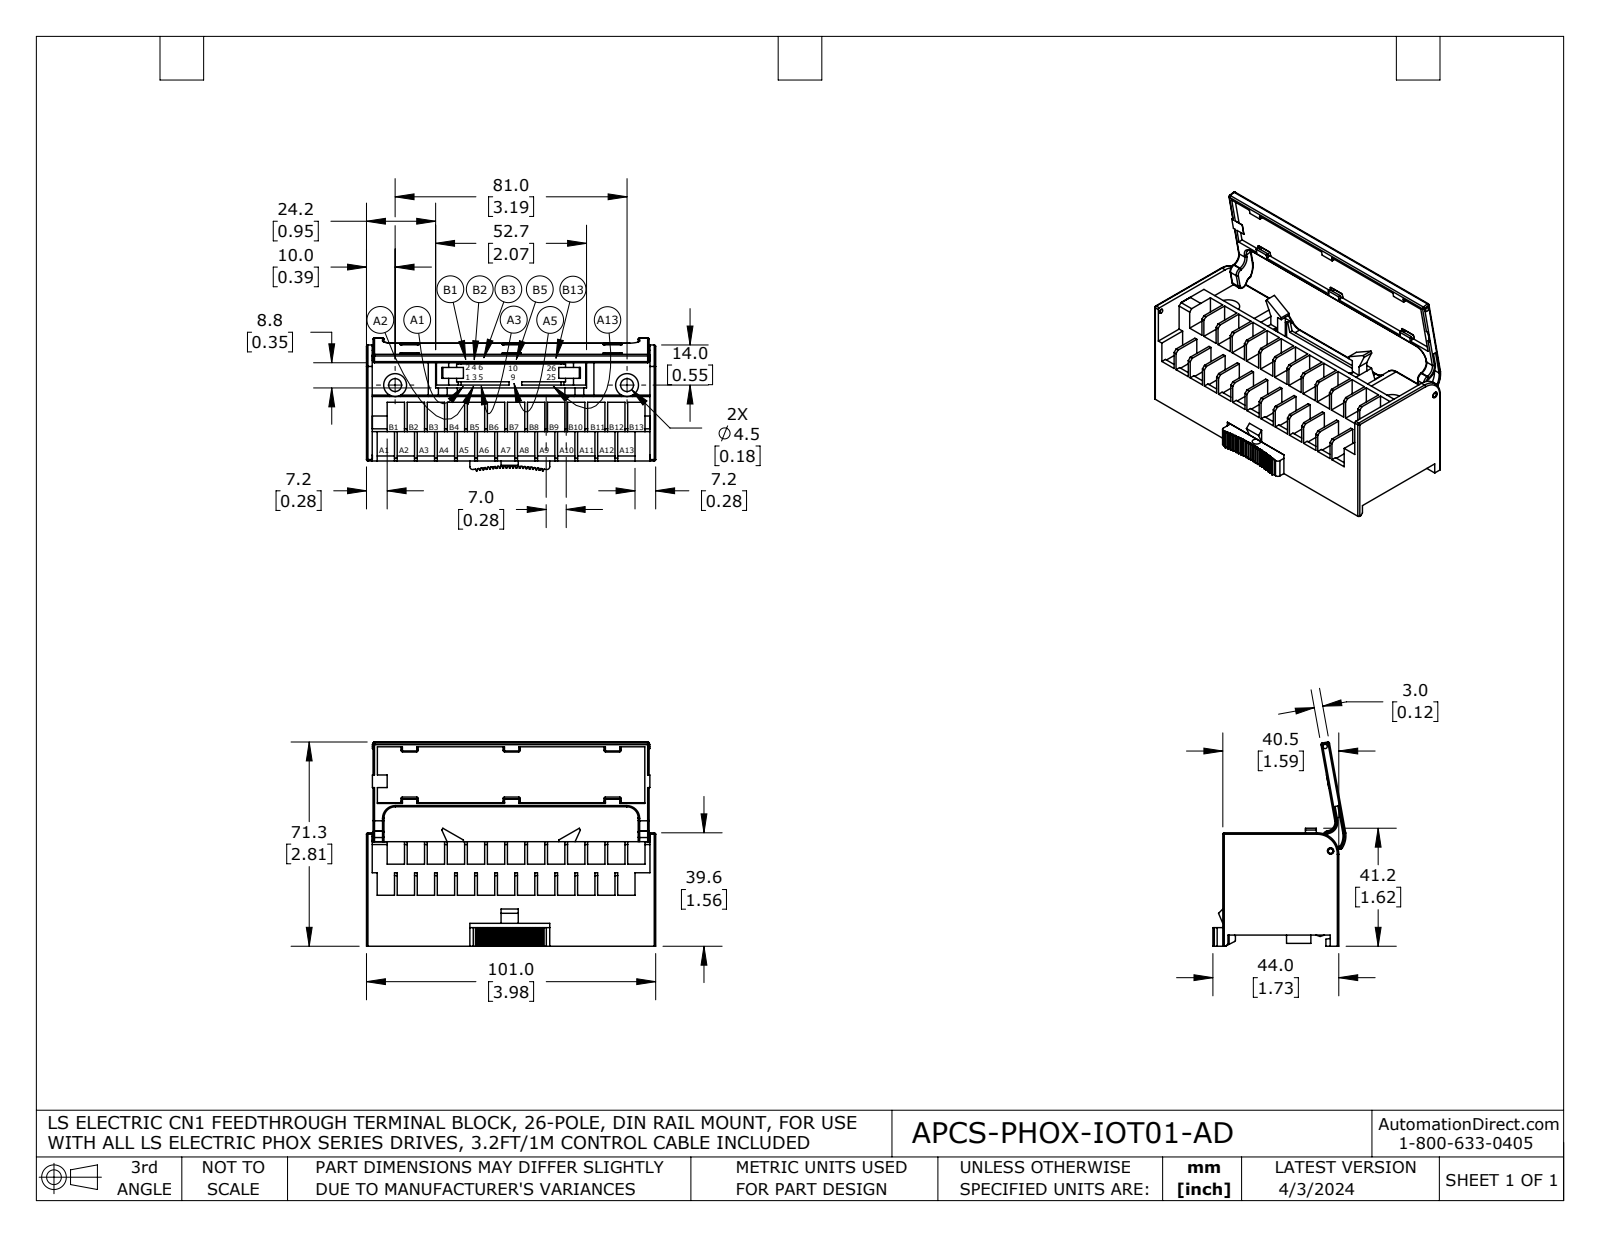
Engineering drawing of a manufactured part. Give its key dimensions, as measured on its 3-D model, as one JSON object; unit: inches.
{"part_name": "APCS-PHOX-IOT01-AD", "step_written_by": "SolidWorks 2021 (AUTOMOTIVE_DESIGN)", "units": "inches", "bodies": {"solids": 2, "faces": 694, "planar": 458, "cylindrical": 175, "other": 61}, "overall_size": [3.976, 1.731, 1.622], "volume_in3": 6.085, "surface_area_in2": 53.63, "round_holes": [[0.177, 2], [0.315, 2], [0.087, 1], [0.118, 1]], "round_bosses_or_shafts": [[0.335, 2], [0.079, 1], [0.059, 1]], "partial_cylinders_radius": [[0.02, 67], [0.157, 5], [0.039, 4], [0.079, 4], [0.197, 4], [0.012, 2], [0.016, 2], [0.217, 2]], "face_to_face_distances": [0.059, 0.404, 1.594, 3.976, 0.551, 0.079, 0.974, 1.587, 0.118, 1.191], "hole_center_spacings": [1.882, 1.912, 3.189]}
